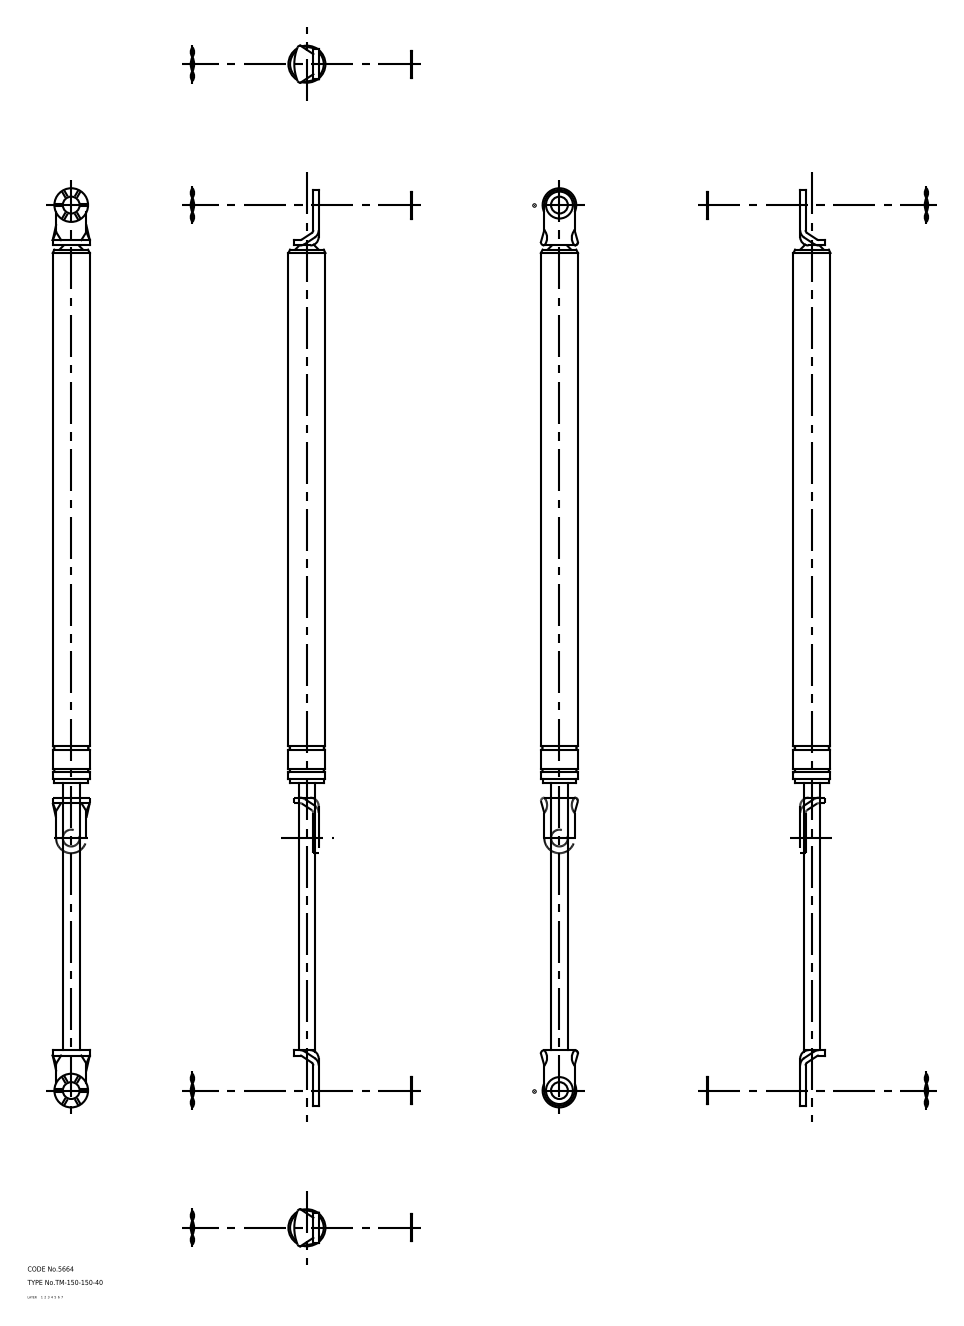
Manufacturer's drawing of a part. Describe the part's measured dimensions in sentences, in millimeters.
The part is named "washer_2; washer_1; body_div". Its 3-D file was written by "spGate 16.7.1 (AUTOMOTIVE_DESIGN)". It is 6 solids with 92 faces: 40 planar, 42 cylindrical and 10 other. Overall it measures 546 by 23 by 22 millimeters. Its volume is 138 158 cubic millimeters and its surface area 33 272 square millimeters. Round holes: 2 of diameter 10. Round bosses or shafts: 3 of diameter 20, 2 of diameter 16, 1 of diameter 22, 1 of diameter 10. Partial cylindrical surfaces (rounded edges, fillets, slot ends): 2 of radius 1.5, 2 of radius 3, 2 of radius 9, 1 of radius 26.32. The main face-to-face distances are 3.2, 2, 5.2, 5.7, 481.2, 3.7, 0.5, 322.2, 162.2, 484.4. The hole center spacings are 526.
